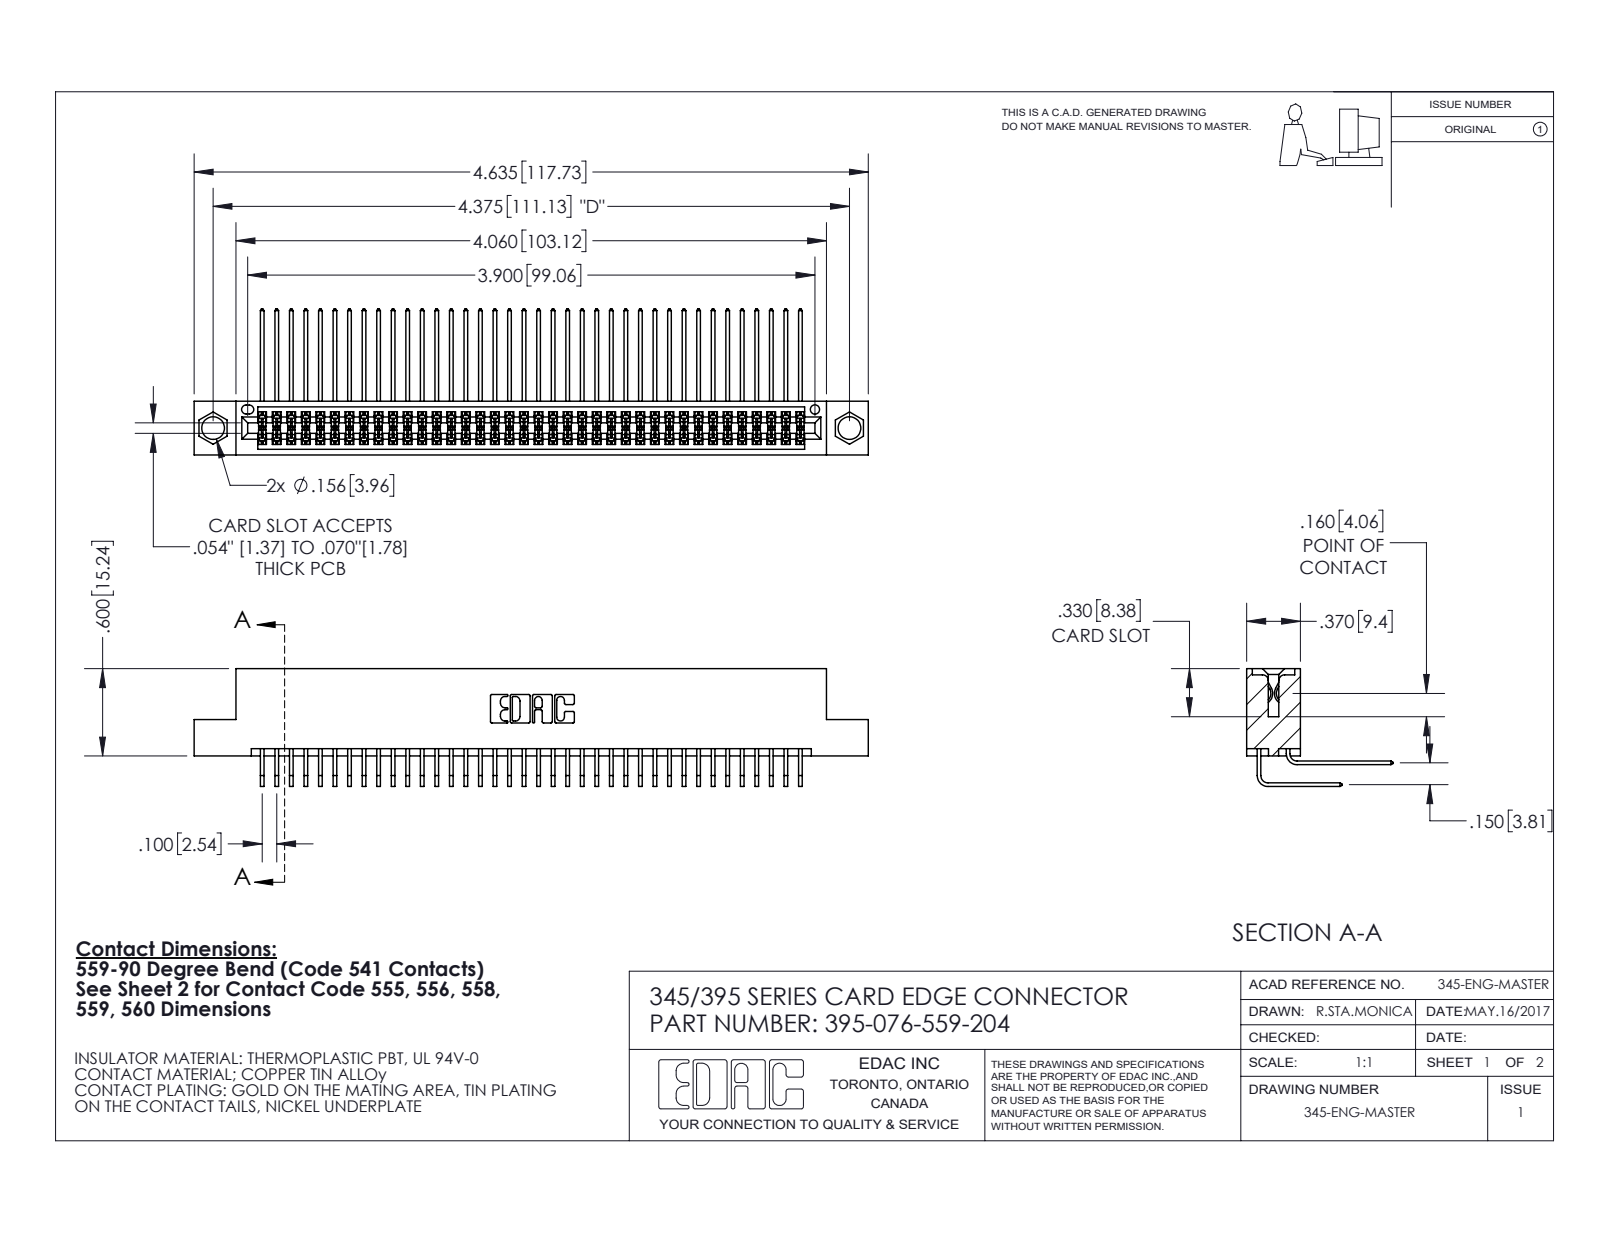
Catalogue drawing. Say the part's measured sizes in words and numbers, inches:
The part is named "345-292-001_558 559 Tail - 1; 345 Part_Flush Mounting Lugs - 0.156 Dia-TI; 345-292-001_559 Tail - 2; 395-076-559-204". Its 3-D file was written by "SolidWorks 2020 (CONFIG_CONTROL_DESIGN)". It is 77 solids with 4092 faces: 2754 planar, 1338 cylindrical and 0 other. Overall it measures 4.635 by 1.005 by 0.809 inches. Its volume is 0.716 cubic inches and its surface area 29.72 square inches. Round holes: 2 of diameter 0.156, 1 of diameter 0.064. Partial cylindrical surfaces (rounded edges, fillets, slot ends): 114 of radius 0.006, 22 of radius 0.01, 6 of radius 0.007, 6 of radius 0.031, 3 of radius 0.026, 2 of radius 0.014, 2 of radius 0.019, 2 of radius 0.022. The main face-to-face distances are 0.072, 0.298, 0.2, 0.37, 0.098, 0.272, 0.025, 0.225, 0.175, 0.15. The hole center spacings are 0.27, 4.139, 4.375.
